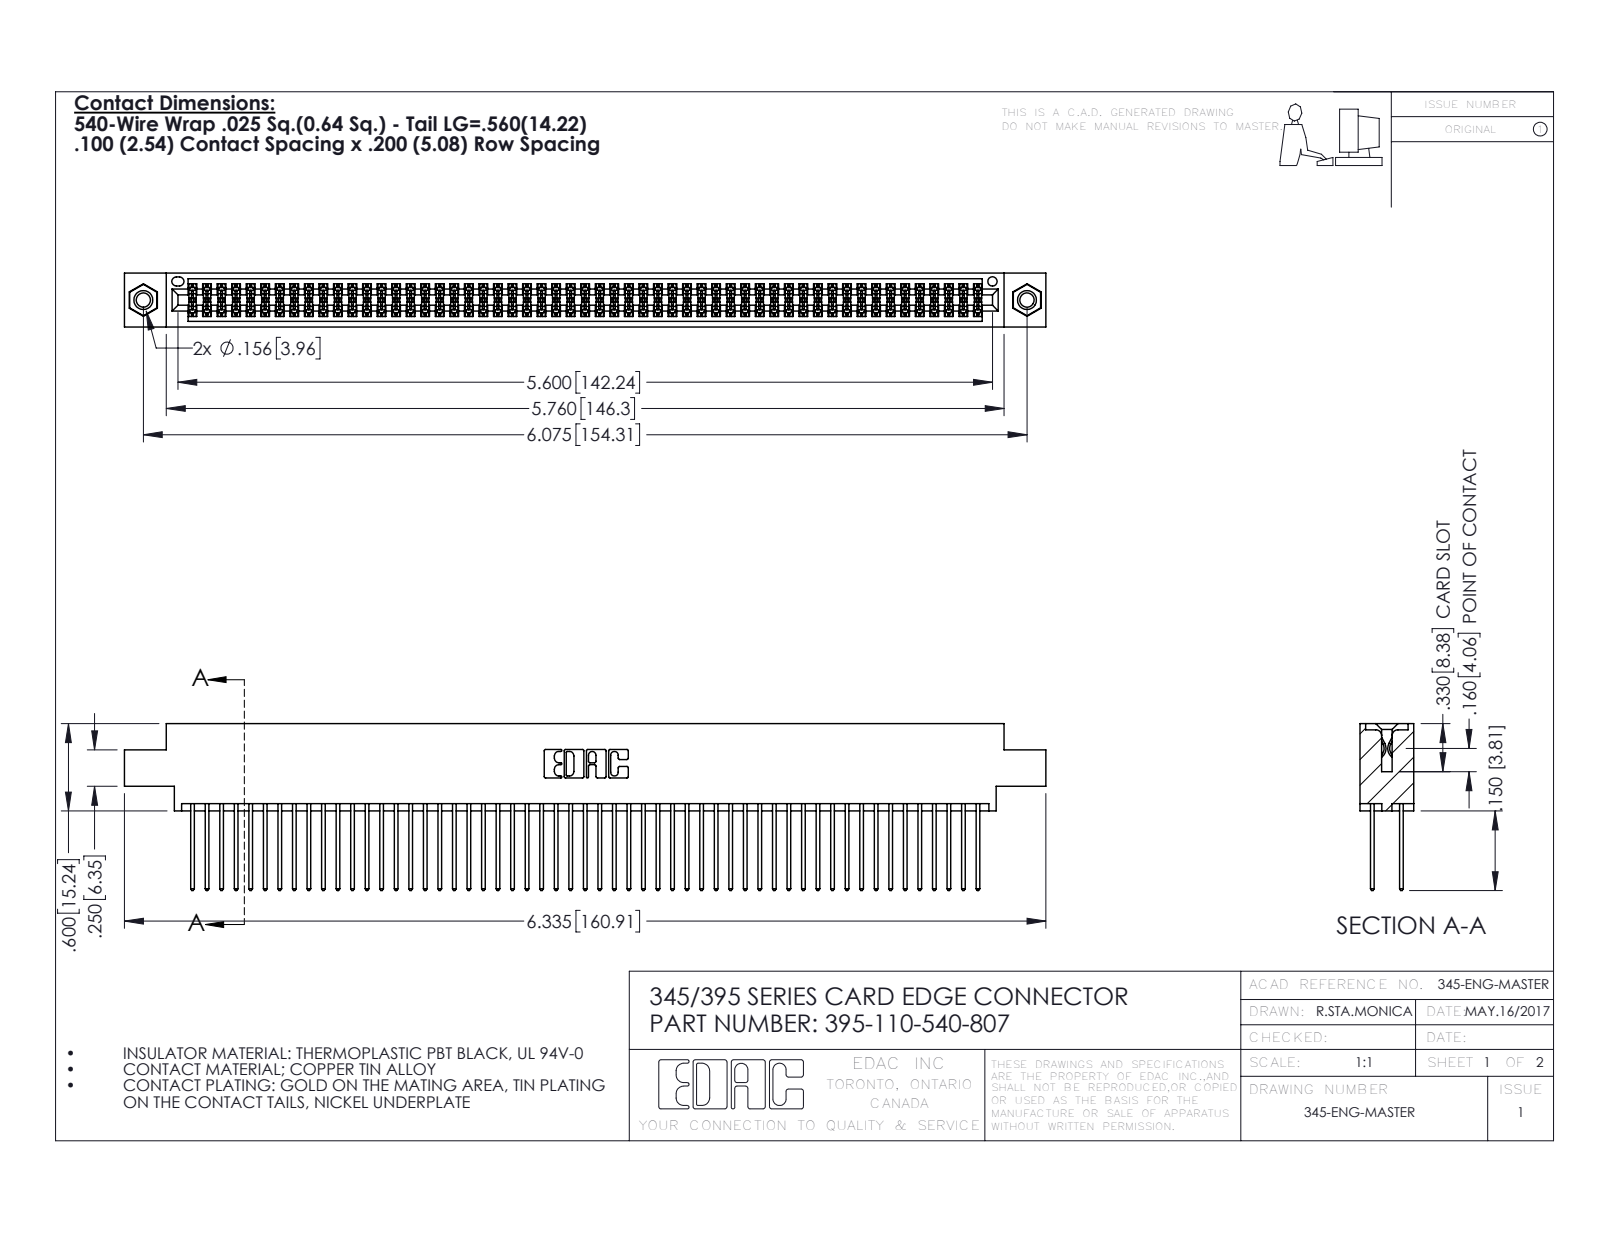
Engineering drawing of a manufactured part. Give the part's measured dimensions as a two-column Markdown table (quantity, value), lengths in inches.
| quantity | value |
| --- | --- |
| part name | 345-250-001_345-250-005-103; 345 Part_0.170 Offset - 0.156 Dia-TI; 395-110-540-807; 345-292-001_345-293-140 |
| STEP written by | SolidWorks 2016 (CONFIG_CONTROL_DESIGN) |
| units | inches |
| bodies | 113 solids, 5690 faces (3746 planar, 1928 cylindrical, 16 other) |
| overall size | 6.335 × 1.147 × 0.37 |
| volume | 0.979 in³ |
| surface area | 40.41 in² |
| round holes (diameter × count) | 0.098 × 2, 0.125 × 2, 0.156 × 2, 0.064 × 1 |
| round bosses / shafts (diameter × count) | 0.155 × 2 |
| partial cylindrical surfaces (radius × count) | 0.006 × 165, 0.01 × 110, 0.01 × 22, 0.007 × 6, 0.031 × 6, 0.026 × 3, 0.014 × 2, 0.019 × 2 |
| main face-to-face distances | 0.072, 0.298, 0.2, 0.098, 0.272, 0.025, 0.37, 0.225, 0.175, 0.149 |
| hole center spacings | 0.27, 5.839, 6.075 |
